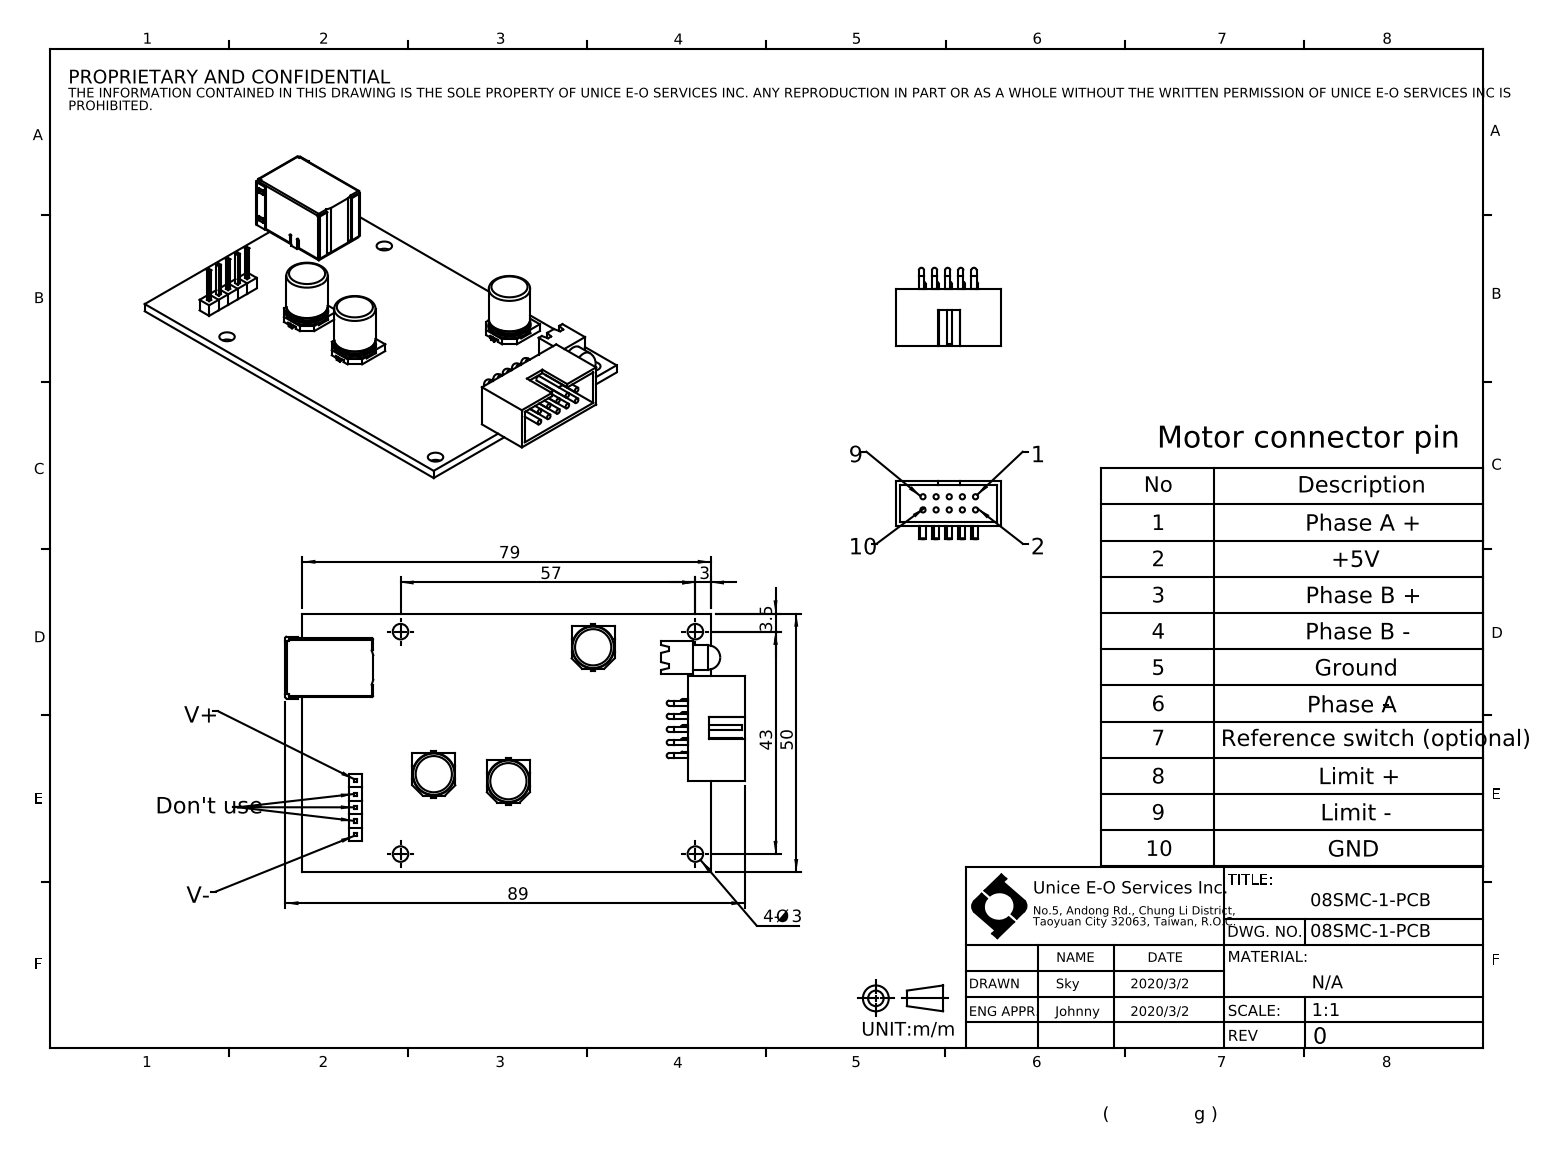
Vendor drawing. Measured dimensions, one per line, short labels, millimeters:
name: 08SMC-1-PCB
written by: SolidWorks 2016 (CONFIG_CONTROL_DESIGN)
unit: mm
bodies: 0 solids, 508 faces (317 planar, 117 cylindrical, 74 other)
size: 88.78 × 50 × 15.42
holes: 4× ⌀3, 3× ⌀8.2
bosses: 35× ⌀1, 3× ⌀8, 3× ⌀7, 1× ⌀4.7
rounds: 7× R0.3, 2× R0.5, 1× R0.25, 1× R3
face distances: 1.7, 0.8, 2.5, 8, 8.8, 10.5, 2.2, 12.7, 11, 10.2
hole spacings: 43, 57, 71.4, 14.48, 16.74, 19.99, 25.17, 28.29
